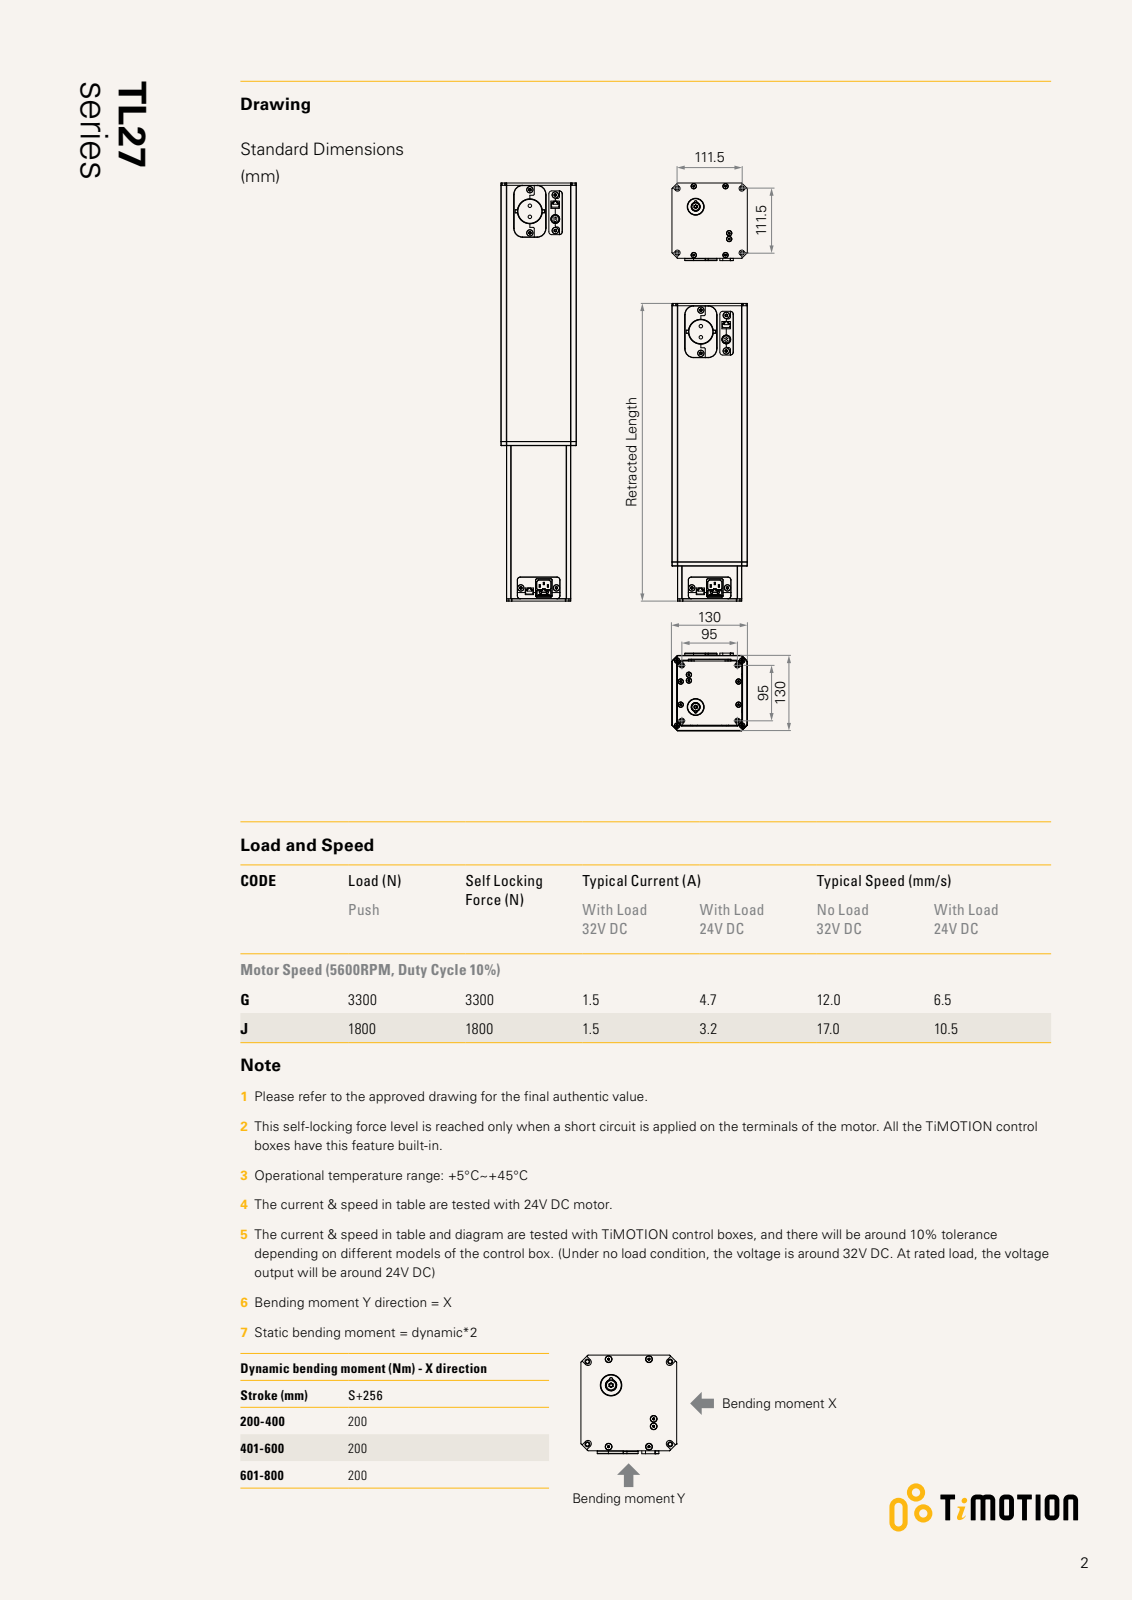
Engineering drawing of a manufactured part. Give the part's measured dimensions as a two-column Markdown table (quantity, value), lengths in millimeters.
| quantity | value |
| --- | --- |
| part name | 三維零件圖-33903-215-12-自攻螺絲; 三維零件圖-31605-809-豎型插座?控盒上蓋-0; 6PIN; 6PINPCB (+8 more) |
| STEP written by | SolidWorks 2015 (CONFIG_CONTROL_DESIGN) |
| units | millimeters |
| bodies | 64 solids, 7046 faces (2725 planar, 2557 cylindrical, 1764 other) |
| overall size | 762.68 × 133 × 129 |
| volume | 2 276 000 mm³ |
| surface area | 1 121 000 mm² |
| round holes (diameter × count) | 4.2 × 30, 6.8 × 12, 9.2 × 12, 5.2 × 8, 5.5 × 8, 6 × 8, 1.09 × 6, 11.5 × 5, 3.3 × 4, 3.4 × 4, 3.5 × 4, 6.2 × 4 |
| round bosses / shafts (diameter × count) | 4 × 12, 7 × 8, 6.5 × 8, 5.4 × 8, 3.9 × 8, 10.5 × 6, 5 × 5, 9 × 4 |
| partial cylindrical surfaces (radius × count) | 0.2 × 600, 0.5 × 184, 0.1 × 103, 1 × 102, 0.3 × 93, 2 × 57, 5 × 25, 3 × 22 |
| main face-to-face distances | 9.5, 119.5, 4, 5.5, 110, 115.5, 129, 114, 1.5, 125 |
| hole center spacings | 103.58, 27.77, 36.49, 67.33, 75.81, 100.88, 111.22, 118.06 |
